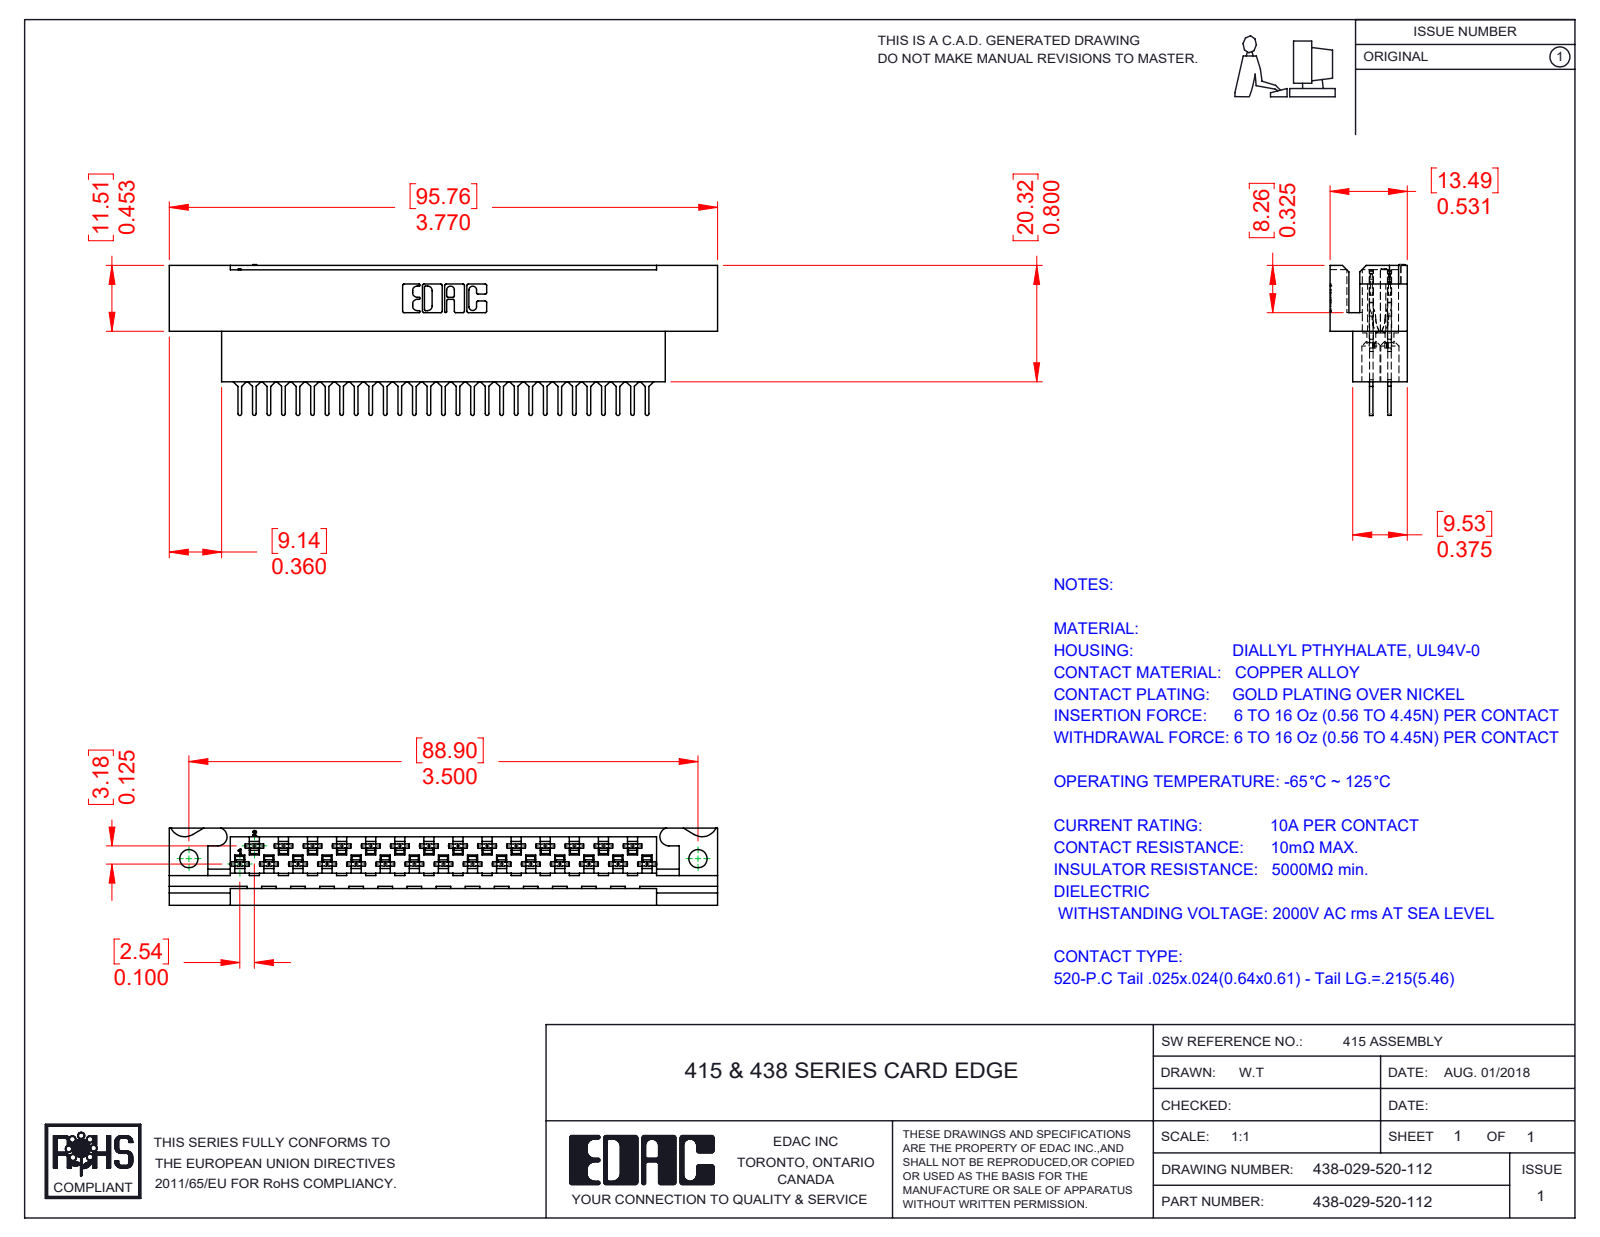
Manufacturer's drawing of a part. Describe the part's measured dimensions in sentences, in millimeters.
The part is named "516-290-001_520; 438-210-001_438-210-029-112; 438-029-520-112". Its 3-D file was written by "SolidWorks 2016 (CONFIG_CONTROL_DESIGN)". It is 30 solids with 2998 faces: 1911 planar, 804 cylindrical and 283 other. Overall it measures 95.76 by 26.32 by 13.49 millimeters. Its volume is 15 522 cubic millimeters and its surface area 19 052 square millimeters. Round holes: 29 of diameter 1.27, 29 of diameter 3.3, 1 of diameter 3.17, 1 of diameter 3.18. Partial cylindrical surfaces (rounded edges, fillets, slot ends): 116 of radius 0.3, 116 of radius 0.56, 58 of radius 0.18, 58 of radius 0.2, 58 of radius 0.41, 58 of radius 2.03, 29 of radius 0.32, 22 of radius 0.25. The main face-to-face distances are 3.18, 1.88, 0.61, 1.27, 13.49, 2.92, 3.96, 7.49, 3.58, 6.76. The hole center spacings are 5.08, 10.16, 15.24, 20.32, 25.4, 30.48, 35.56, 2.54.
